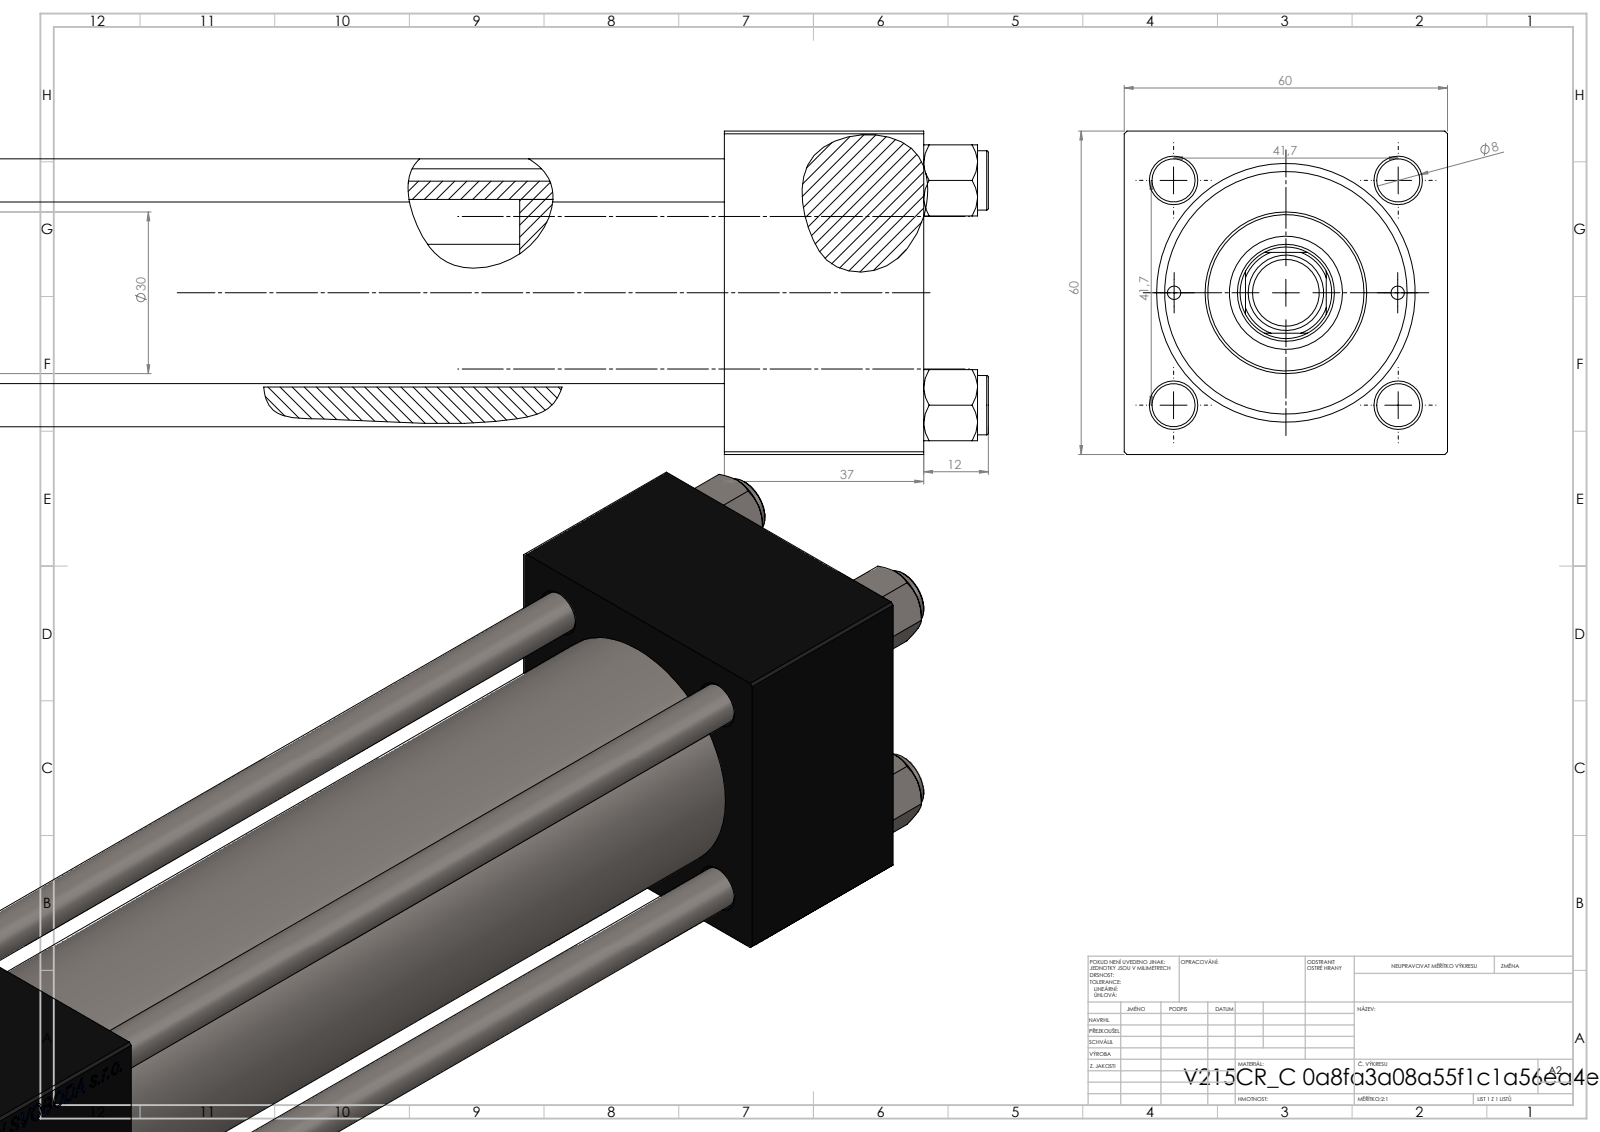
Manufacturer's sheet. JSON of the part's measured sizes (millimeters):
{"part_name": "V215CR_C_Body; V215CR_VCP_C; V215_VC_A; V215CR_C_TYCINKA (+2 more)", "step_written_by": "SolidWorks 2019 (CONFIG_CONTROL_DESIGN)", "units": "millimeters", "bodies": {"solids": 12, "faces": 1168, "planar": 532, "cylindrical": 94, "other": 542}, "overall_size": [308, 60, 60], "volume_mm3": 495576, "surface_area_mm2": 151396, "round_holes": [[8, 4], [2.5, 2], [7, 2], [16.66, 2], [24, 2], [8.5, 1], [18, 1], [21, 1], [31, 1], [40, 1], [45, 1]], "round_bosses_or_shafts": [[11, 4], [46, 1], [30, 1], [14, 1], [12, 1]], "partial_cylinders_radius": [[8.5, 1]], "face_to_face_distances": [60, 37, 253, 216, 53, 200, 163, 224.3, 187.3, 24.3], "hole_center_spacings": [20.85, 29.49, 41.7, 46.53, 20.75, 58.97, 41.5, 197.5]}
